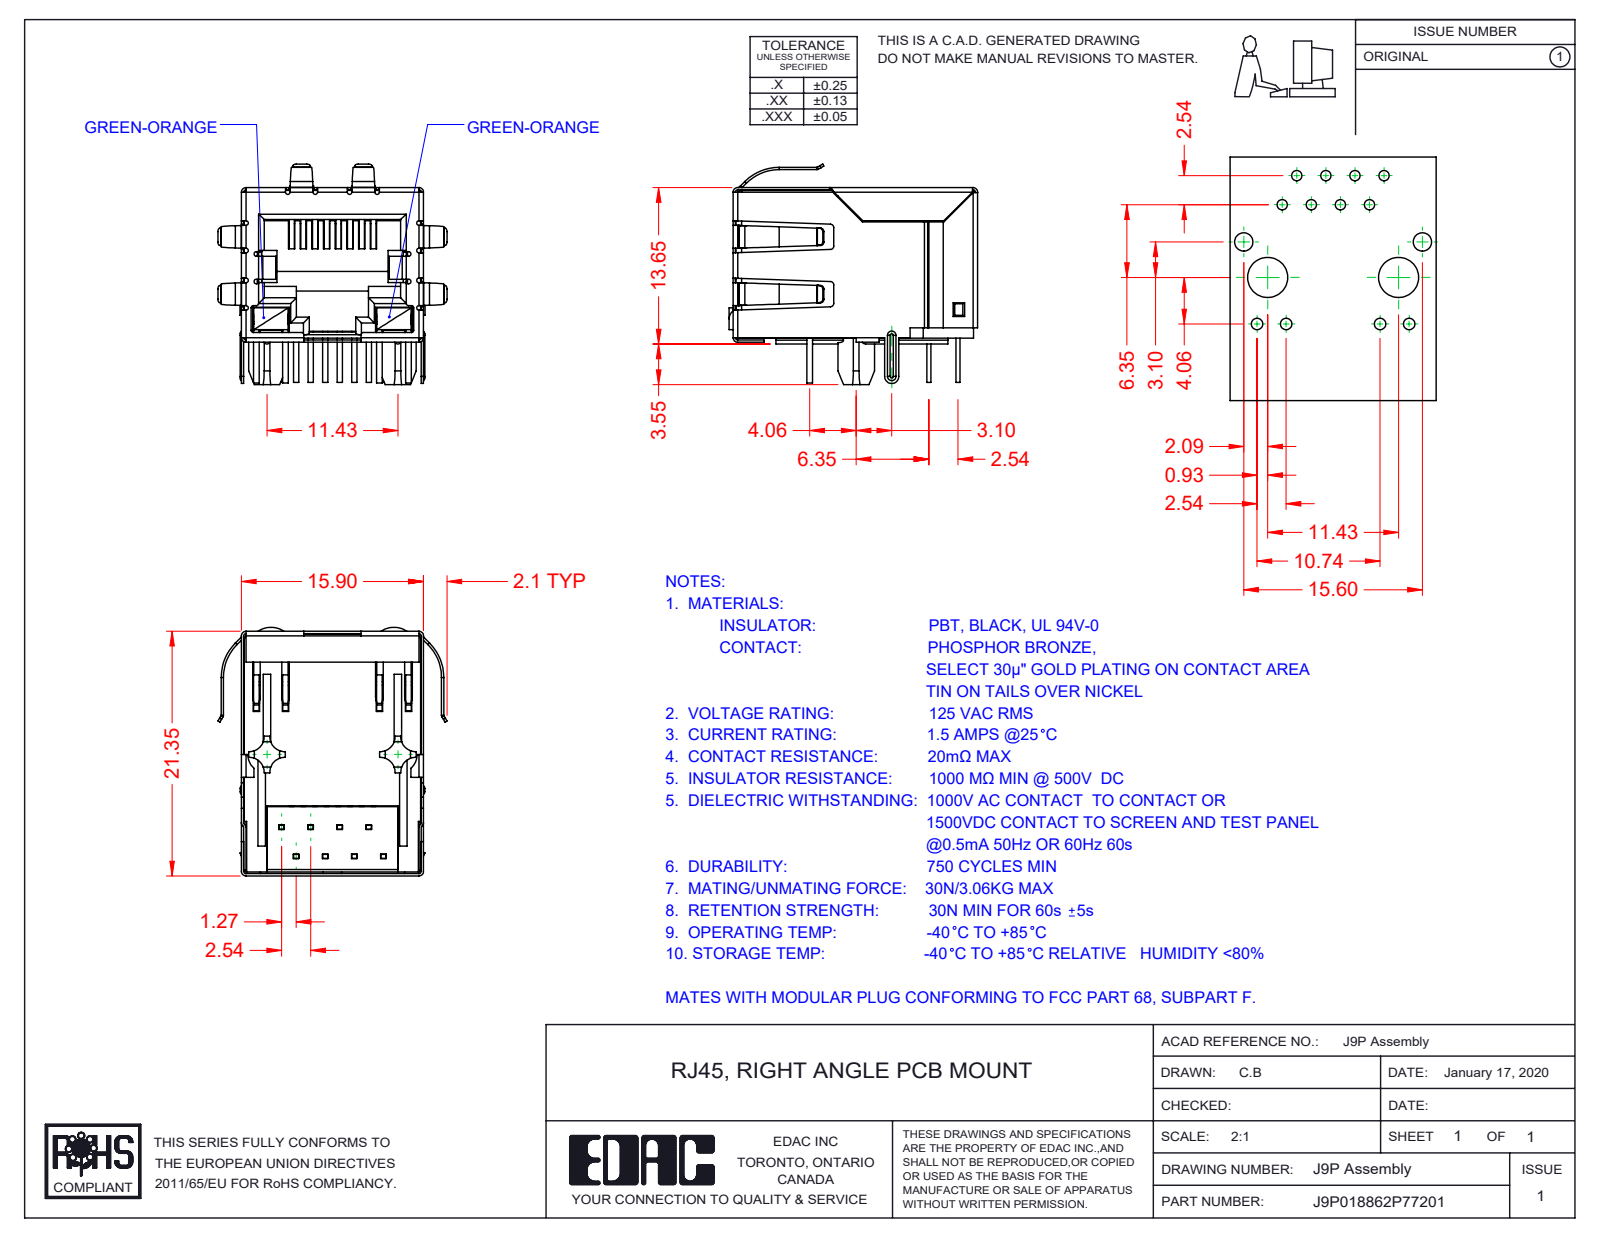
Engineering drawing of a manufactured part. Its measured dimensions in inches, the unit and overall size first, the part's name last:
Units: inches
Overall size (bounding box): 0.854 × 0.787 × 0.758
Partial cylindrical surfaces — rounded edges, fillets, slot ends (radius × count): R0.008 ×39, R0.02 ×22, R0.012 ×20, R0.016 ×16, R0.051 ×8, R0.009 ×5, R0.004 ×4, R0.012 ×4
Main face-to-face distances: 0.608, 0.618, 0.616, 0.014, 0.021, 0.61, 0.487, 0.024, 0.055, 0.023
Volume: 0.164 in³ · Surface area: 11.65 in²
Bodies: 13 solids, 1476 faces (1042 planar, 340 cylindrical, 94 other)
Part name (STEP PRODUCT): 9P-LED LED RH_7-Green-Orange; J9P018862P77202; 9P-LED Assembly; 9P-LED Contacts (+4 more)
STEP written by: SolidWorks 2016 (CONFIG_CONTROL_DESIGN)
